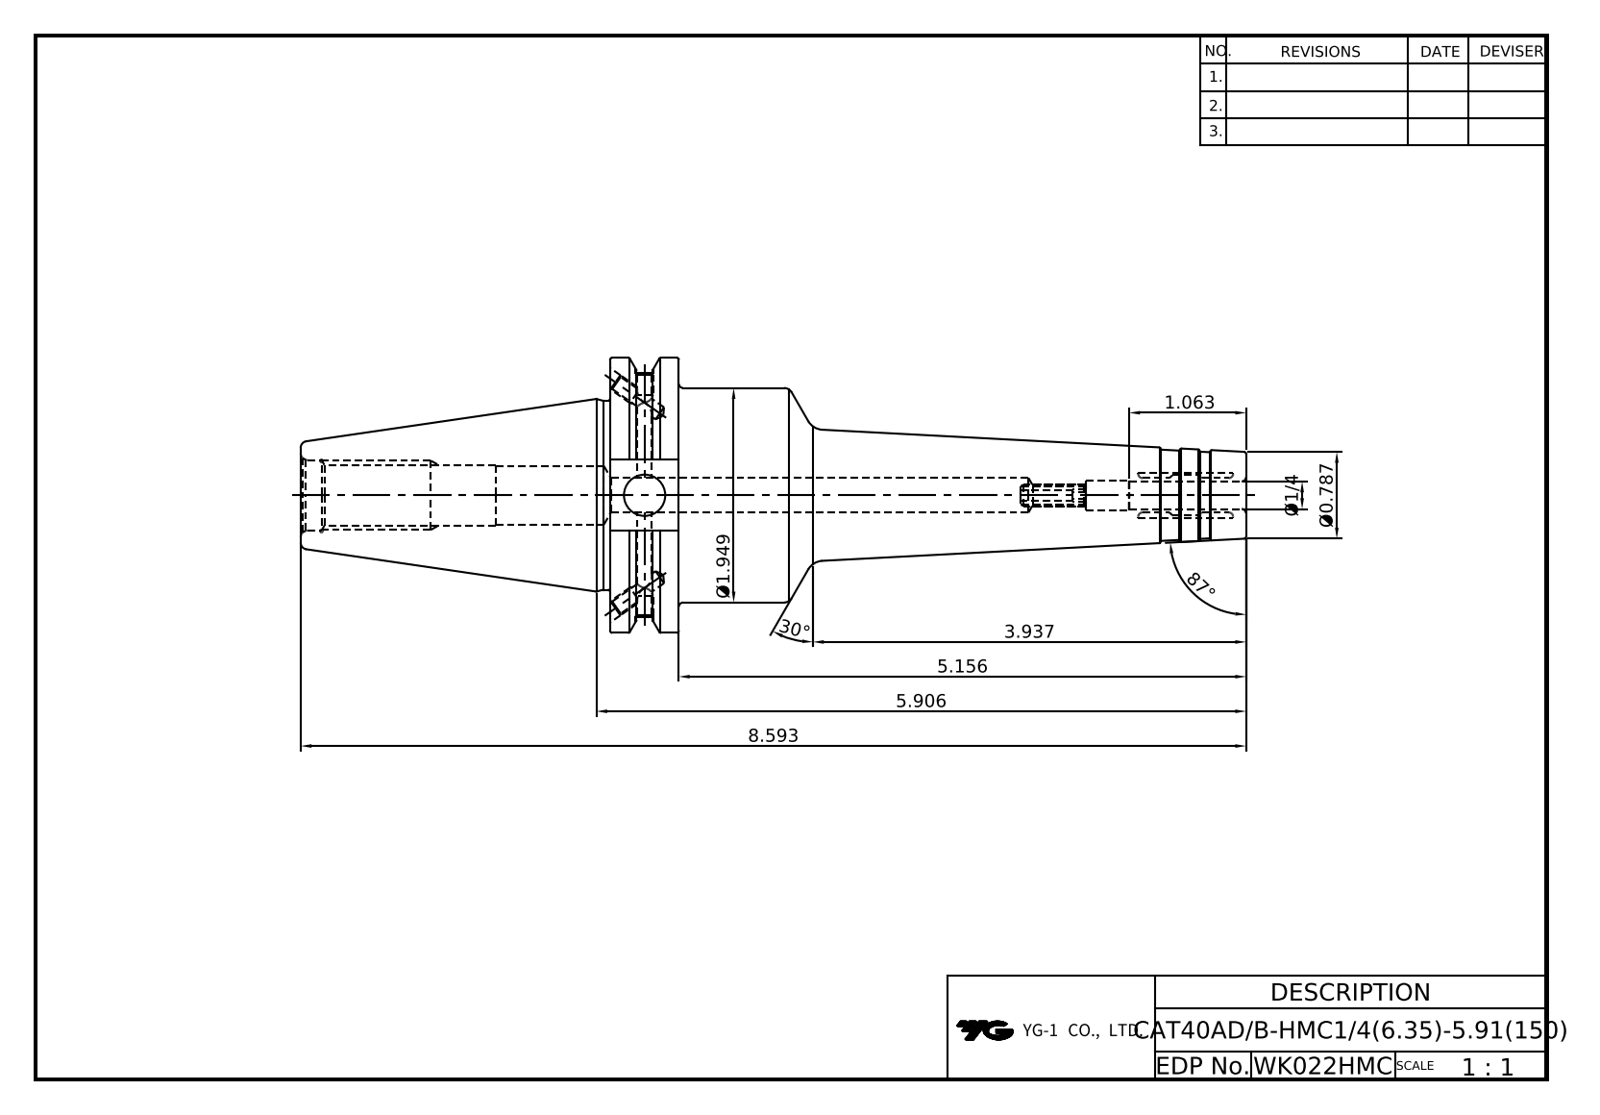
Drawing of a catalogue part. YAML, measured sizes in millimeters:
part_name: "CAT40ADB-SHANK"
step_written_by: "CREO PARAMETRIC BY PTC INC, 2018500 (CONFIG_CONTROL_DESIGN)"
units: millimeters
bodies: {solids: 1, faces: 143, planar: 37, cylindrical: 28, other: 78}
overall_size: [218.28, 63.5, 60.84]
volume: 203592
surface_area: 36685
round_holes:
  - {diameter: 4.2, count: 1}
  - {diameter: 5, count: 1}
  - {diameter: 6.35, count: 1}
  - {diameter: 6.8, count: 1}
  - {diameter: 8, count: 1}
  - {diameter: 9.53, count: 1}
  - {diameter: 13.49, count: 1}
  - {diameter: 15.88, count: 1}
  - {diameter: 16.3, count: 1}
round_bosses_or_shafts:
  - {diameter: 63.5, count: 1}
  - {diameter: 56.3, count: 1}
  - {diameter: 49.5, count: 1}
  - {diameter: 43.6, count: 1}
face_to_face_distances: [15.9, 146.86, 130.96, 47.6, 71.42, 87.32, 218.28, 16.38, 77.47, 6.05]
